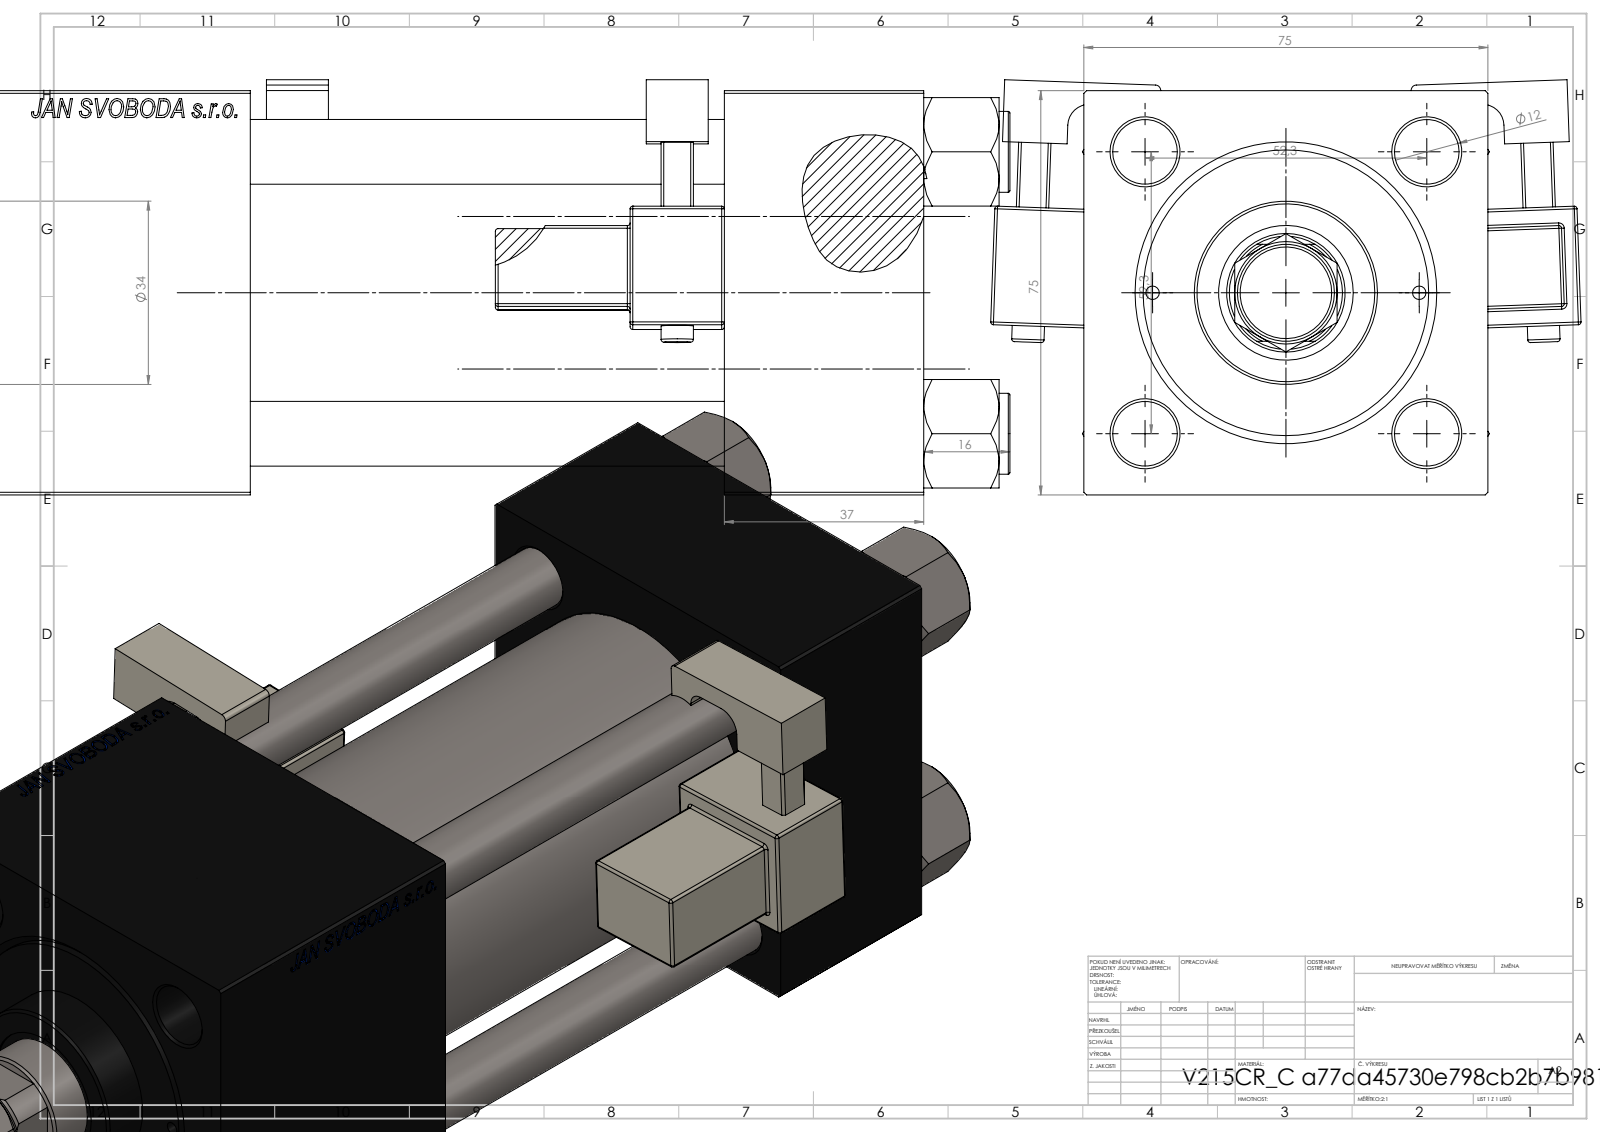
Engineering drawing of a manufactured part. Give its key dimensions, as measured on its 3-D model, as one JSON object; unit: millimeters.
{"part_name": "V215_VC_A; V215CR_C_Body; V215CR_C_TYCINKA; NUT_M5_C (+3 more)", "step_written_by": "SolidWorks 2019 (CONFIG_CONTROL_DESIGN)", "units": "millimeters", "bodies": {"solids": 14, "faces": 1360, "planar": 602, "cylindrical": 154, "other": 604}, "overall_size": [258, 109.57, 77.03], "volume_mm3": 746090, "surface_area_mm2": 178918, "round_holes": [[12, 4], [2.5, 2], [7, 2], [20.96, 2], [30, 2], [10.5, 1], [22, 1], [25, 1], [41, 1], [50, 1], [53, 1]], "round_bosses_or_shafts": [[15, 4], [6, 2], [56, 1], [34, 1], [18, 1], [11, 1]], "partial_cylinders_radius": [[0.5, 48], [1, 2], [2.5, 2], [4, 2], [10.5, 1]], "face_to_face_distances": [75, 37, 59, 184, 147, 125, 88, 155.3, 118.3, 30.3], "hole_center_spacings": [26.19, 36.98, 52.3, 57.22, 24.75, 73.96, 49.5, 123.5]}
